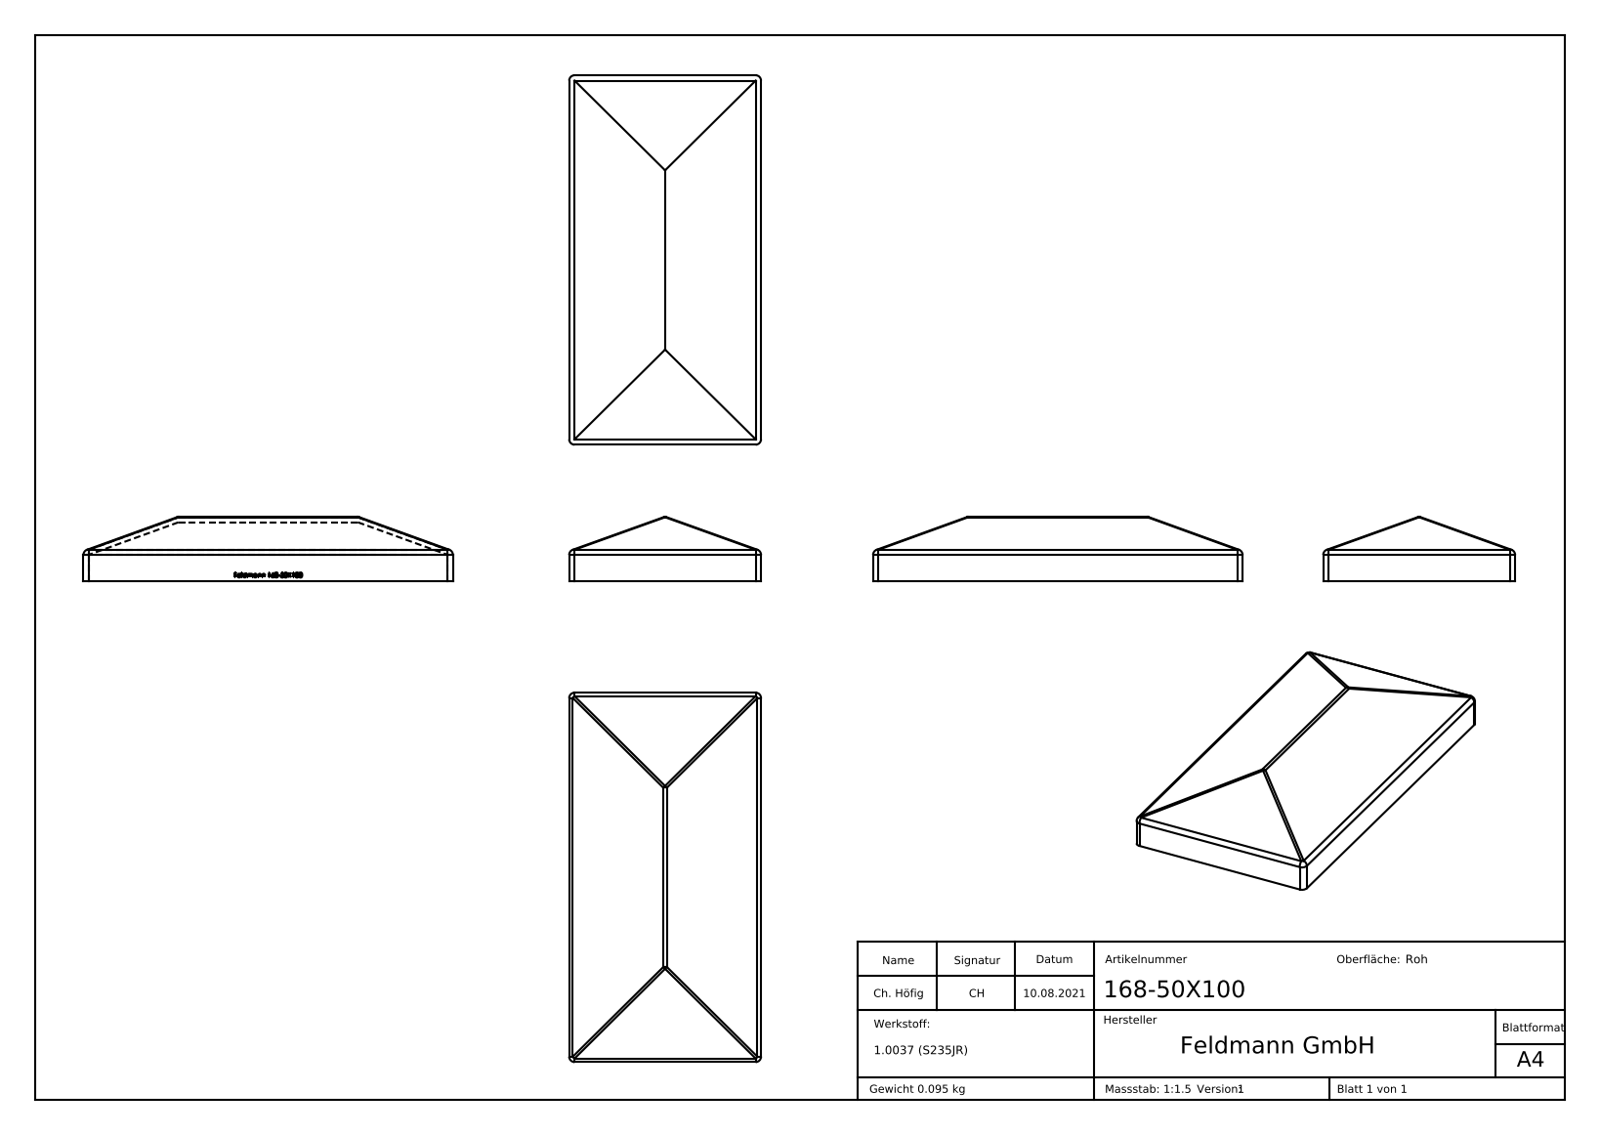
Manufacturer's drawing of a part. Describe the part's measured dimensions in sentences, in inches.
The part is named "168-50X100". Its 3-D file was written by "SolidWorks 2018 (CONFIG_CONTROL_DESIGN)". It is 1 solid with 265 faces: 135 planar, 13 cylindrical and 117 other. Overall it measures 4.094 by 2.126 by 0.709 inches. Its volume is 0.742 cubic inches and its surface area 25.87 square inches. Partial cylindrical surfaces (rounded edges, fillets, slot ends): 13 of radius 0.059. The main face-to-face distances are 0.059, 2.067, 4.035, 2.126, 2.008, 4.094, 3.976, 0.055, 2.012, 2.071.
